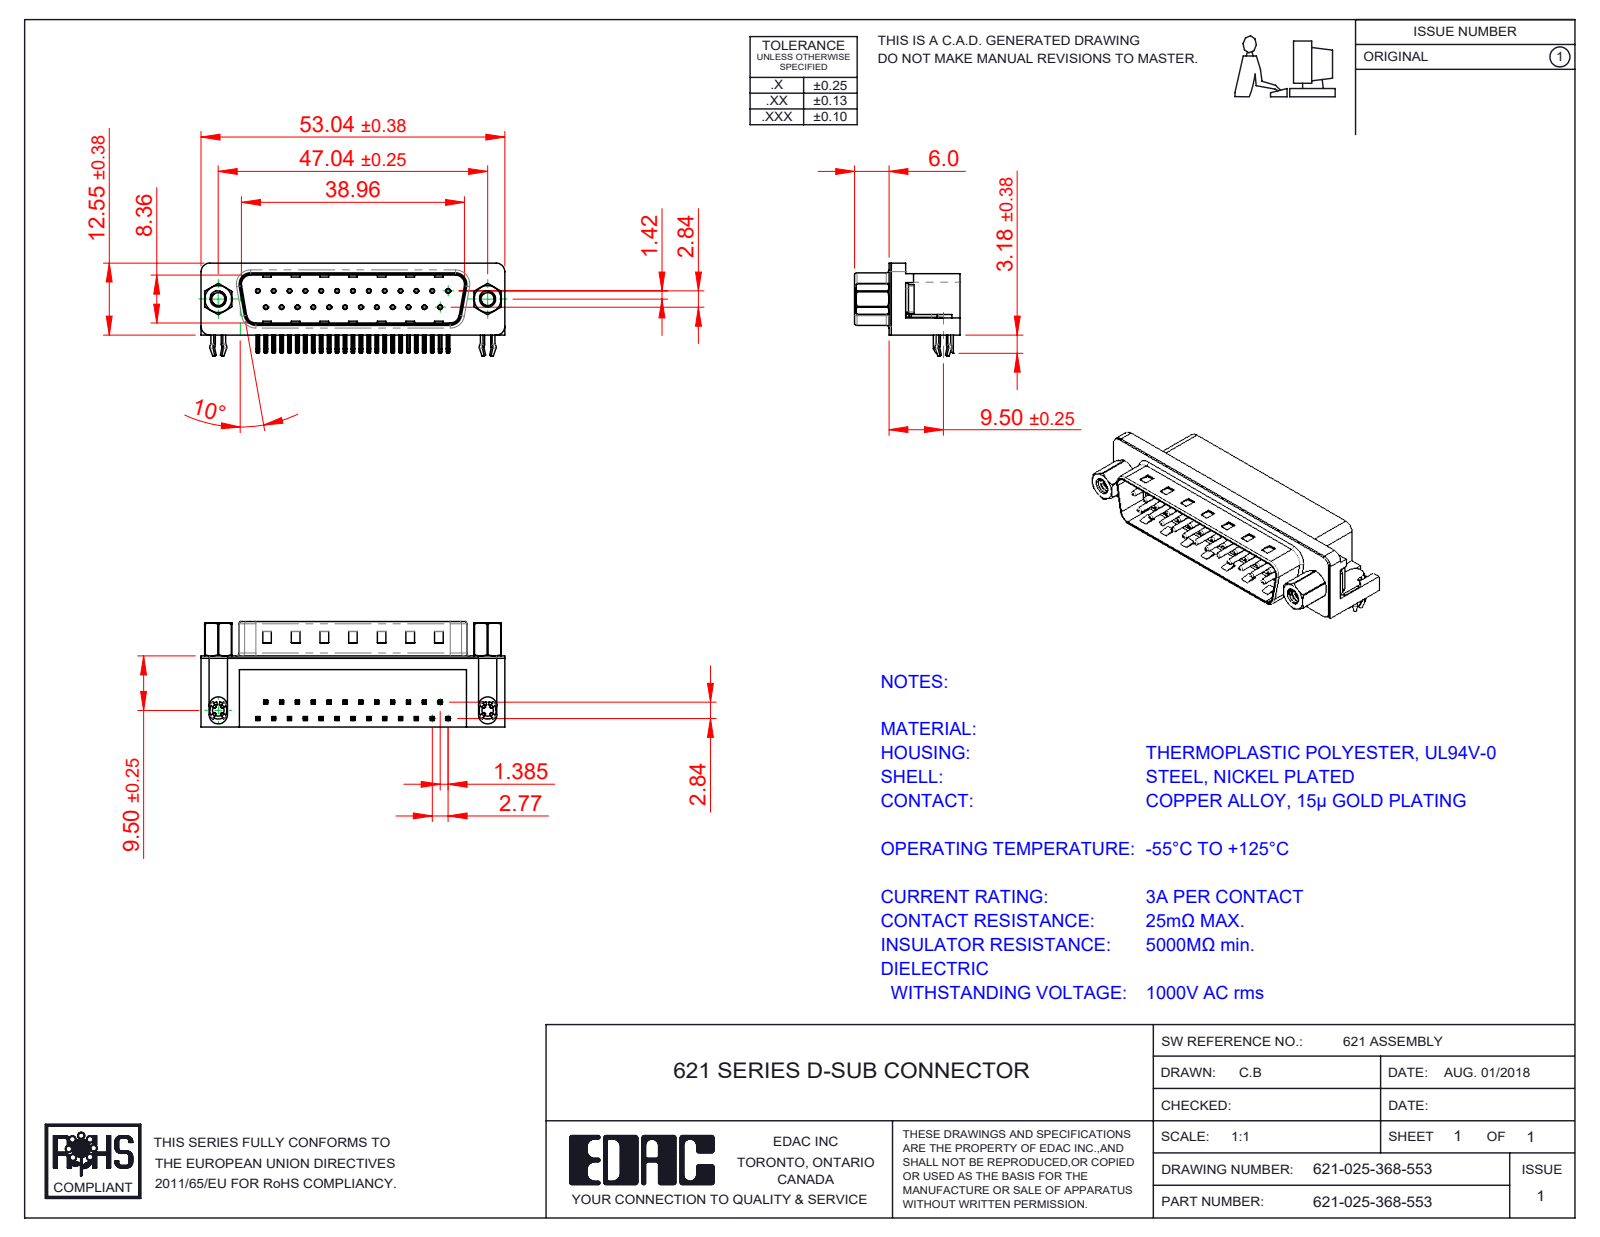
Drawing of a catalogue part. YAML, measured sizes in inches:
part_name: "621-025-368-553; 621 Housing_25 Socket; 621 4-40 Threaded Board Mount; 621 Shell_25 Socket (+4 more)"
step_written_by: "SolidWorks 2016 (CONFIG_CONTROL_DESIGN)"
units: inches
bodies: {solids: 33, faces: 2419, planar: 1427, cylindrical: 743, other: 249}
overall_size: [2.088, 0.724, 0.619]
volume: 0.401
surface_area: 12.78
round_holes:
  - {diameter: 0.014, count: 25}
  - {diameter: 0.031, count: 25}
  - {diameter: 0.089, count: 4}
  - {diameter: 0.09, count: 2}
  - {diameter: 0.157, count: 2}
  - {diameter: 0.189, count: 2}
  - {diameter: 0.197, count: 2}
round_bosses_or_shafts:
  - {diameter: 0.03, count: 25}
  - {diameter: 0.193, count: 2}
  - {diameter: 0.187, count: 2}
  - {diameter: 0.154, count: 2}
  - {diameter: 0.128, count: 2}
  - {diameter: 0.11, count: 2}
partial_cylinders:
  - {radius: 0.01, count: 108}
  - {radius: 0.005, count: 50}
  - {radius: 0.039, count: 16}
  - {radius: 0.02, count: 9}
  - {radius: 0.063, count: 8}
  - {radius: 0.059, count: 7}
  - {radius: 0.035, count: 4}
  - {radius: 0.079, count: 4}
face_to_face_distances: [0.016, 0.472, 0.407, 0.083, 0.345, 0.412, 0.067, 0.428, 0.488, 0.354]
hole_center_spacings: [0.124, 0.109, 0.218, 0.327, 0.436, 0.545, 0.654, 0.198]
